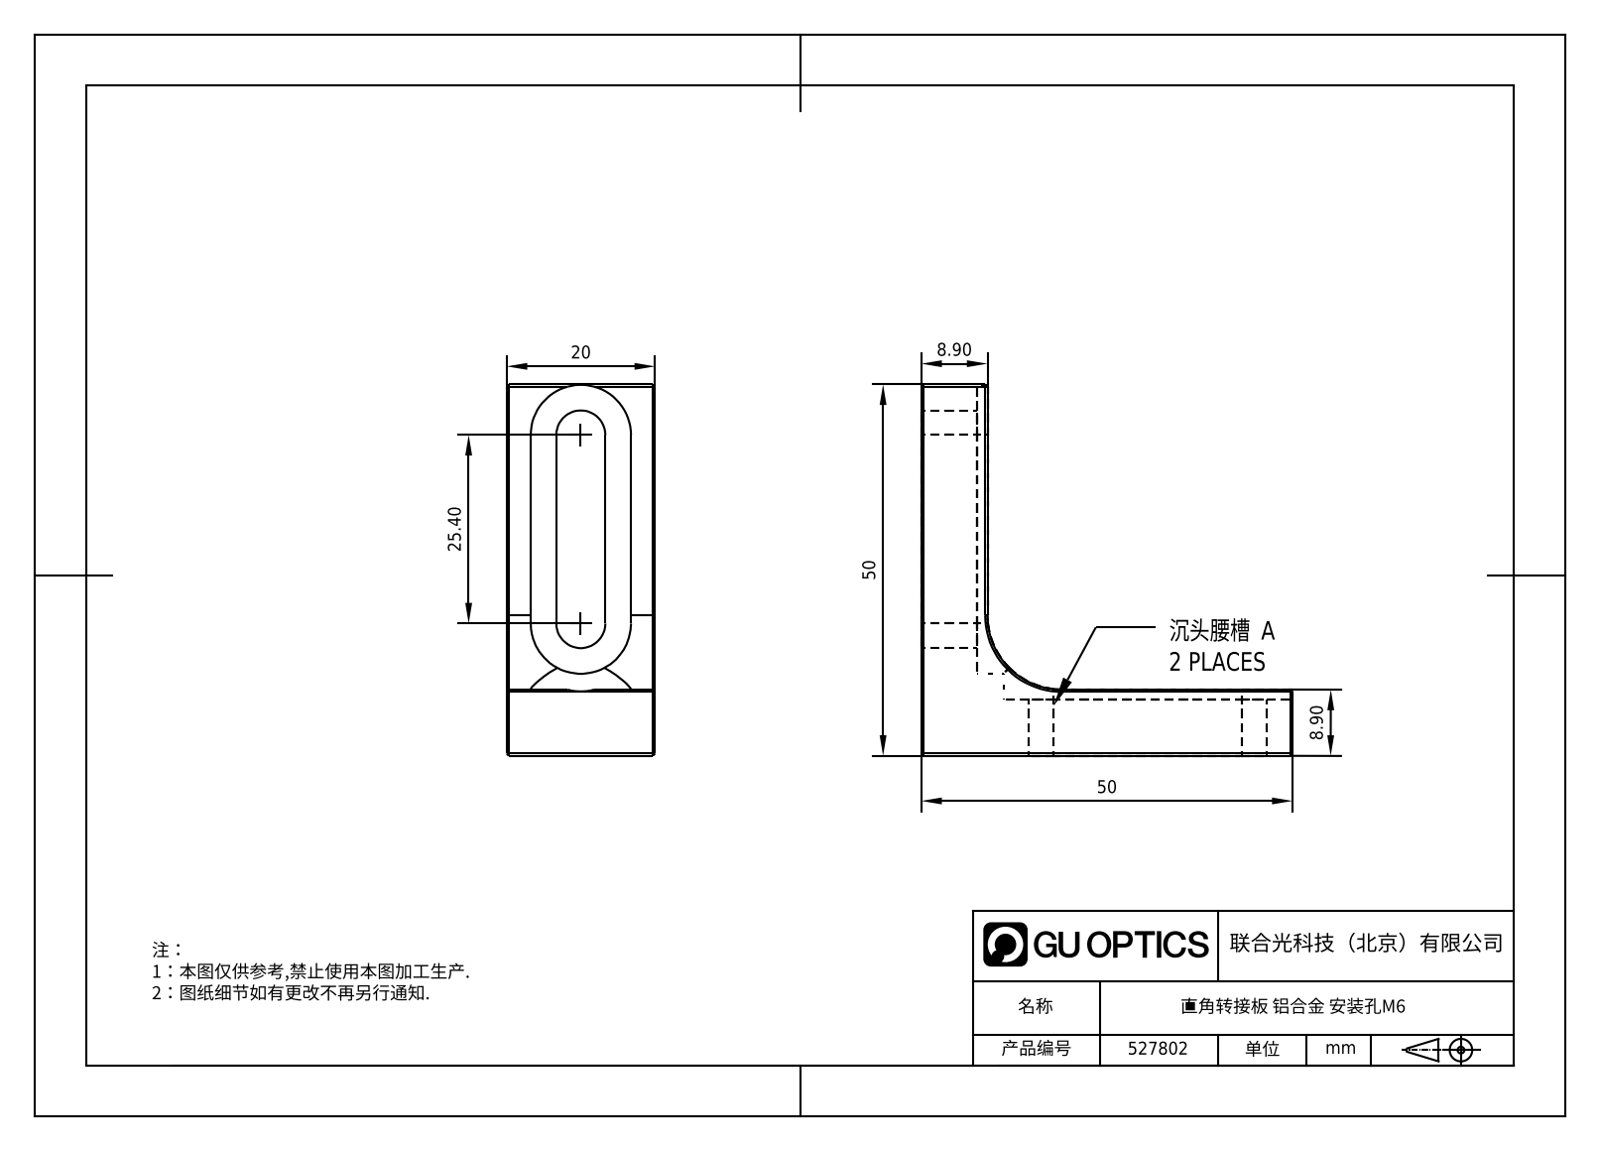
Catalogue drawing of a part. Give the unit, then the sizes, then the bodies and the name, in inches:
Units: inches
Overall size (bounding box): 1.969 × 1.969 × 0.787
Partial cylindrical surfaces — rounded edges, fillets, slot ends (radius × count): R0.13 ×4, R0.266 ×4, R0.394 ×1
Main face-to-face distances: 0.787, 0.264, 0.524, 0.295, 0.35, 0.055, 0.26, 1.969, 1.673, 1.618
Volume: 0.738 in³ · Surface area: 9.419 in²
Bodies: 1 solid, 63 faces (47 planar, 14 cylindrical, 2 other)
Part name (STEP PRODUCT): 7.5.4.4-MCS-50A
STEP written by: SolidWorks 2021 (CONFIG_CONTROL_DESIGN)
